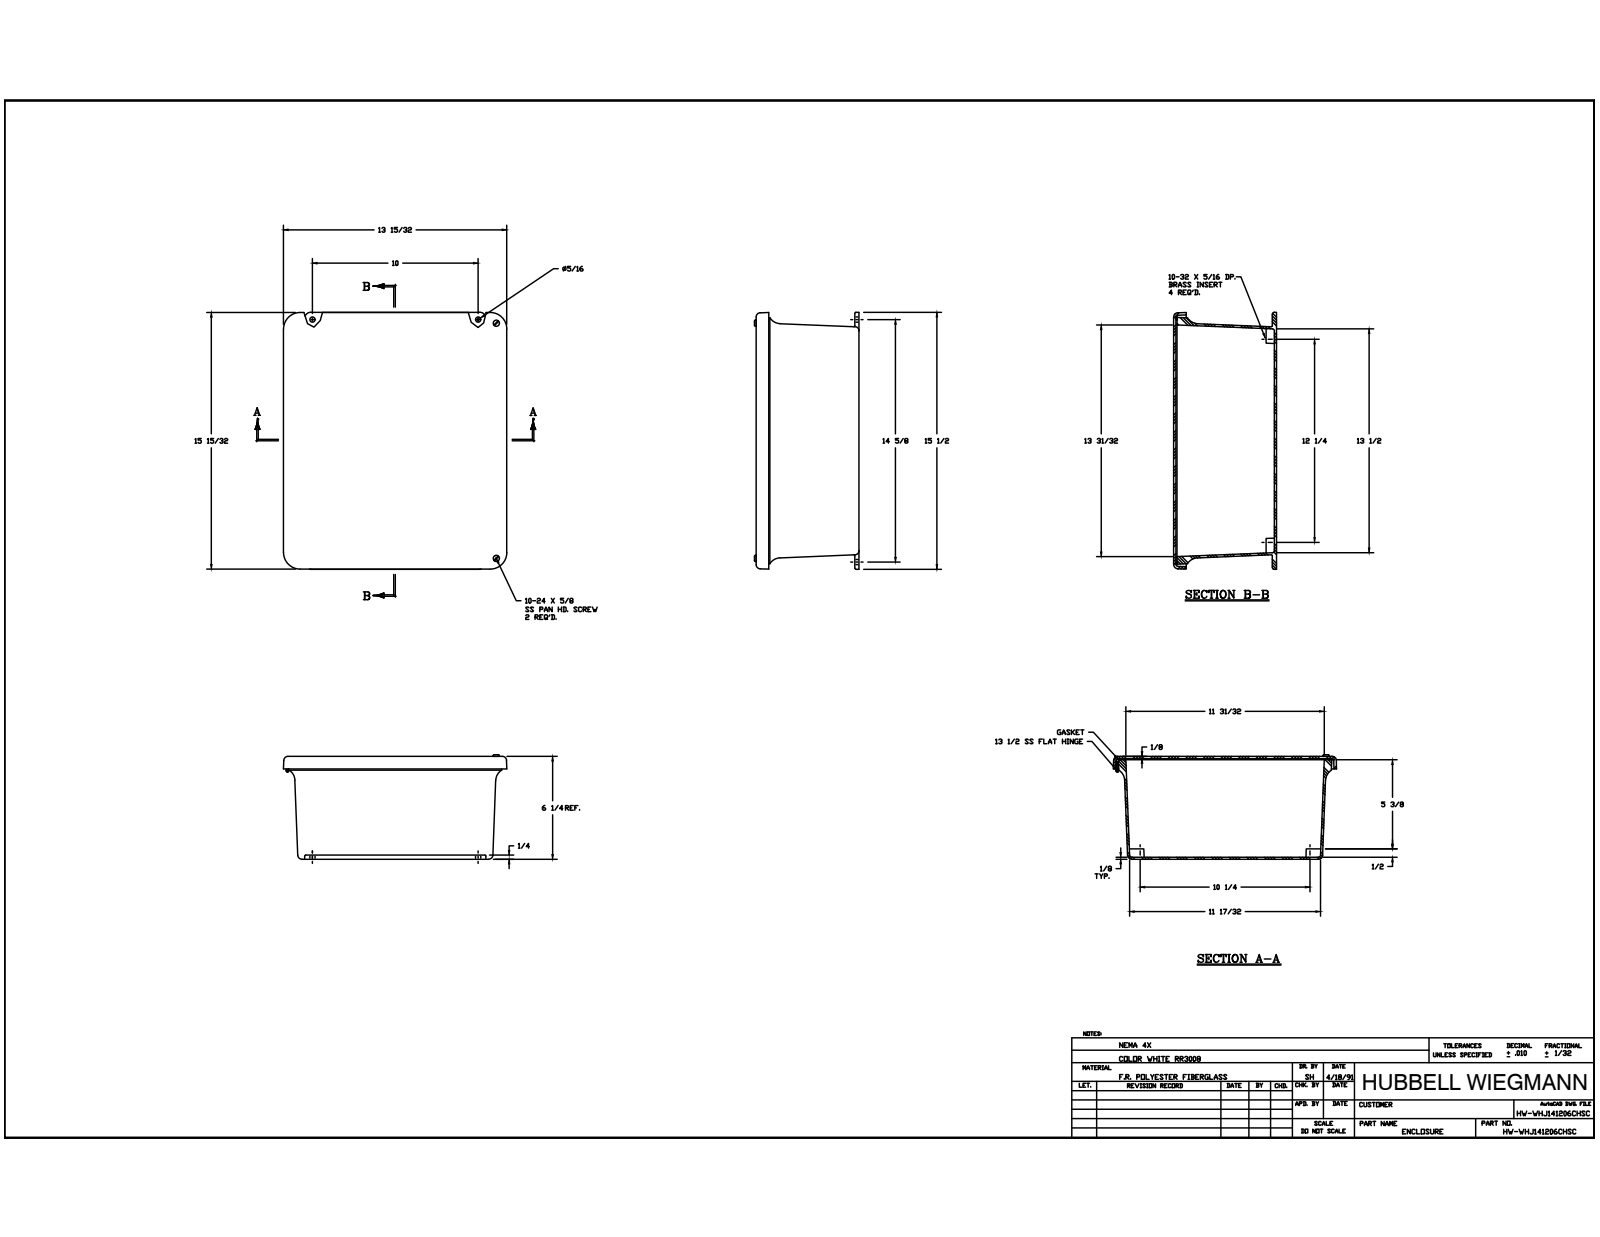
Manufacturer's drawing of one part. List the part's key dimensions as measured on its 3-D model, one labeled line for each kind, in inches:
Part name (STEP PRODUCT): J1412HW_1; RMINS45821P_191; RMINS45821P_192; RMINS45821P_193 (+8 more)
STEP written by: Autodesk Inventor 2014 (AUTOMOTIVE_DESIGN)
Units: inches
Bodies: 24 solids, 858 faces (317 planar, 334 cylindrical, 207 other)
Overall size (bounding box): 15.5 × 13.504 × 6.344
Volume: 113 in³ · Surface area: 1 570 in²
Round holes (diameter × count): ⌀0.131 ×10, ⌀0.14 ×10, ⌀0.152 ×8, ⌀0.156 ×4, ⌀0.218 ×4, ⌀0.145 ×2, ⌀0.085 ×1
Round bosses / shafts (diameter × count): ⌀0.25 ×10, ⌀0.125 ×10, ⌀0.27 ×6, ⌀0.19 ×2, ⌀0.156 ×2, ⌀0.155 ×1
Partial cylindrical surfaces — rounded edges, fillets, slot ends (radius × count): R0.031 ×20, R0.125 ×12, R0.25 ×12, R0.2 ×4, R0.375 ×4, R0.75 ×4, R0.063 ×2
Main face-to-face distances: 0.125, 0.135, 6.078, 6.213, 5.953, 6.087, 0.125, 0.33, 0.152, 6
Hole centre spacings: 3.25, 6.5, 9.75, 0.25, 3, 1.37, 6.25, 11.26
